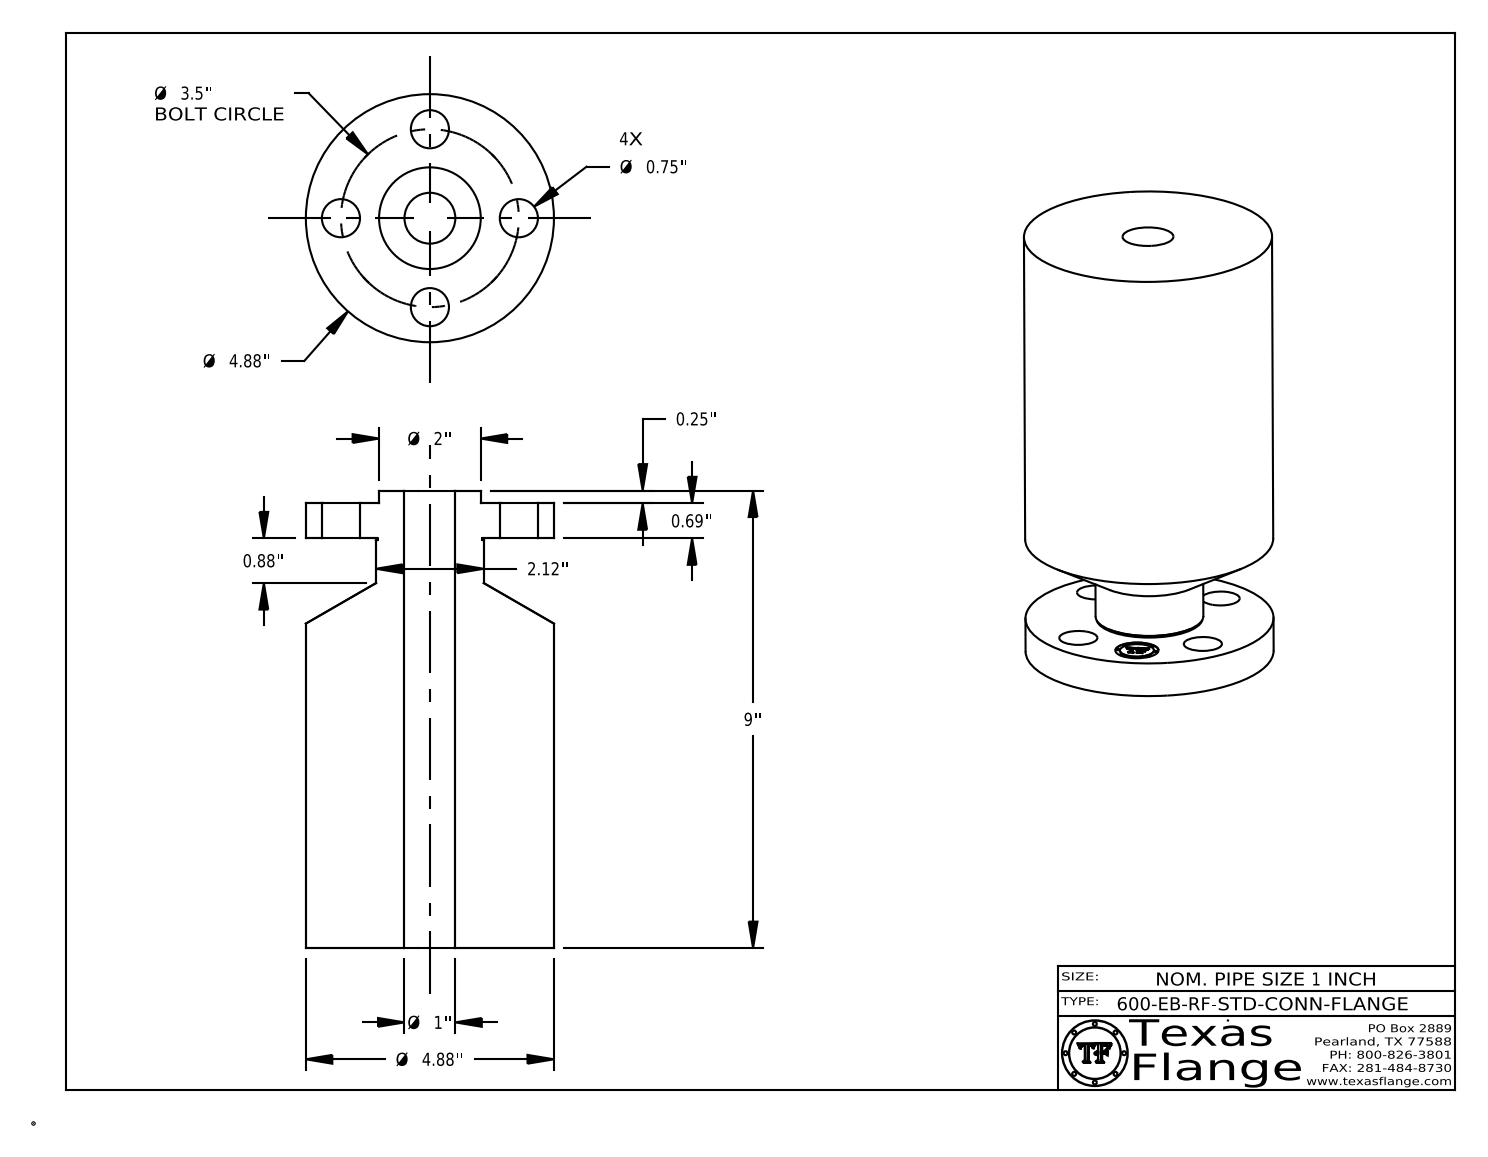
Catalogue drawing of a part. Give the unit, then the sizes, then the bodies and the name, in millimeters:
Units: millimetres
Overall size (bounding box): 228.6 × 124 × 124
Round holes (diameter × count): ⌀19.1 ×4, ⌀21.6 ×1, ⌀25.4 ×1
Round bosses / shafts (diameter × count): ⌀1.3 ×8, ⌀124 ×1, ⌀53.8 ×1, ⌀50.8 ×1, ⌀17 ×1
Main face-to-face distances: 222.3, 17.5, 204.7, 6.4, 23.9, 228.6, 23.7, 17.4, 204.9, 0.4
Hole centre spacings: 44.5, 62.9, 34, 82.1, 88.9
Volume: 2 229 000 mm³ · Surface area: 139 400 mm²
Bodies: 1 solid, 413 faces (369 planar, 38 cylindrical, 6 other)
Part name (STEP PRODUCT): 1-600-EB-RF-STD-CONN-FLANGE
STEP written by: CATIA V5 STEP AP214 (AUTOMOTIVE_DESIGN)
